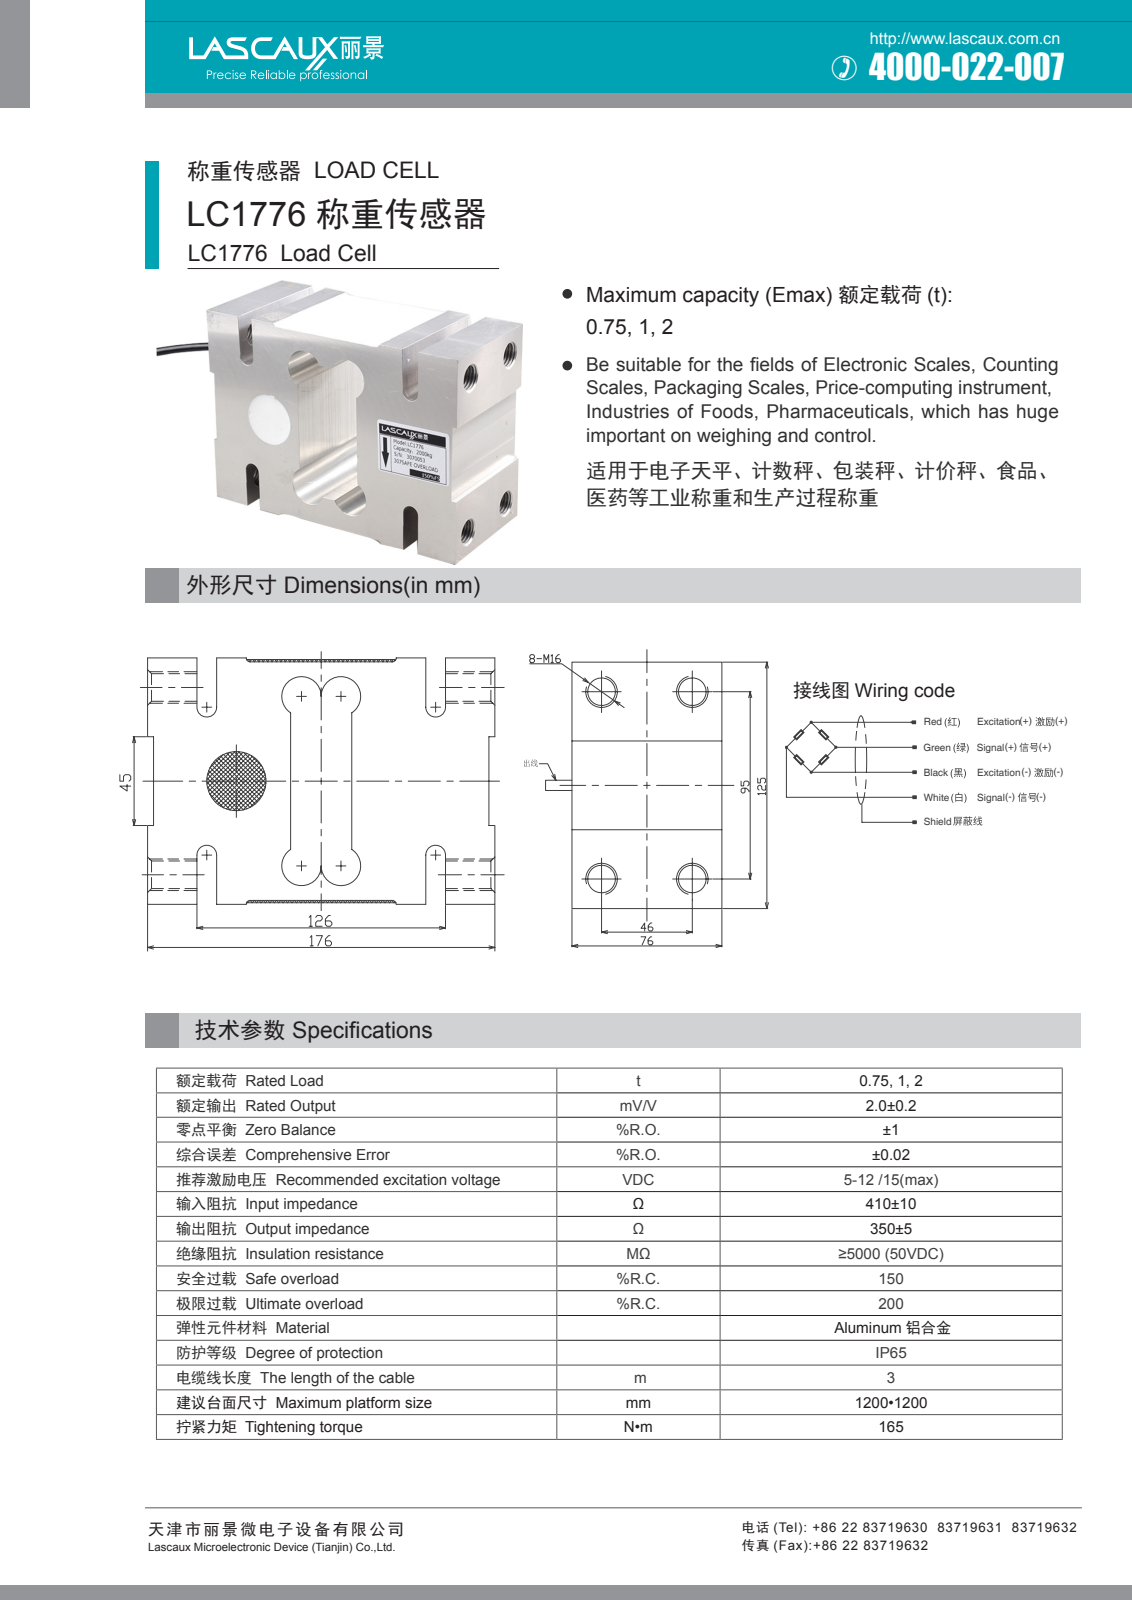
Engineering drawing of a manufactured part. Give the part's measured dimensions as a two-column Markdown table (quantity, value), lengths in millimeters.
| quantity | value |
| --- | --- |
| part name | 传感器LC1776 |
| STEP written by | SolidWorks 2016 (CONFIG_CONTROL_DESIGN) |
| units | millimeters |
| bodies | 1 solid, 71 faces (39 planar, 32 cylindrical, 0 other) |
| overall size | 176 × 125 × 96 |
| volume | 1 273 000 mm³ |
| surface area | 127 303 mm² |
| round holes (diameter × count) | 14 × 4 |
| round bosses / shafts (diameter × count) | 8 × 1 |
| partial cylindrical surfaces (radius × count) | 1 × 4, 5 × 4, 8.5 × 4 |
| main face-to-face distances | 76, 69, 32, 123, 2, 72, 104, 35, 141, 37 |
| hole center spacings | 46, 95, 105.55 |
